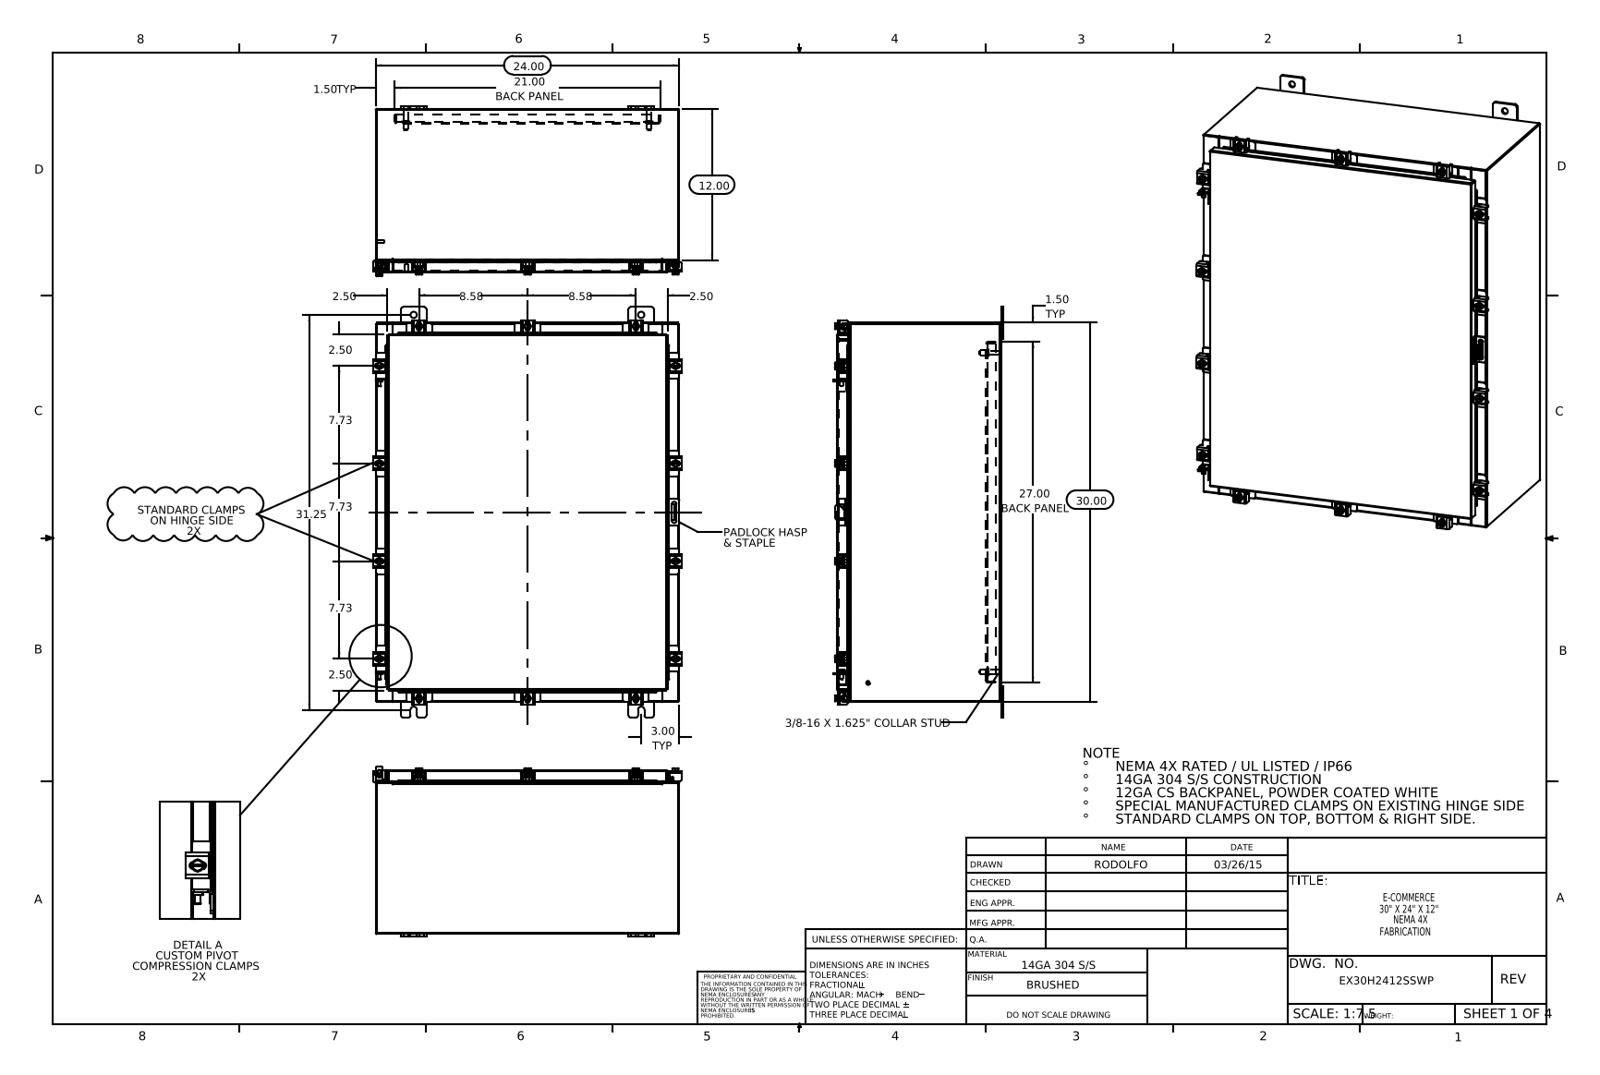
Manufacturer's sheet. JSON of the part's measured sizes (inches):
{"part_name": "Quarter-20 CD Stud; EX30H2412SSWP Cover; Clamp Top_RTP31; EX30H2412SSWP (+8 more)", "step_written_by": "SolidWorks 2014 (CONFIG_CONTROL_DESIGN)", "units": "inches", "bodies": {"solids": 91, "faces": 2272, "planar": 1211, "cylindrical": 885, "other": 176}, "overall_size": [32.5, 24.421, 13.453], "volume_in3": 296.7, "surface_area_in2": 7434, "round_holes": [[0.213, 14], [0.26, 14], [0.5, 8], [0.125, 1], [0.25, 1]], "round_bosses_or_shafts": [[0.5, 14], [0.25, 14], [0.399, 12], [0.625, 4], [0.375, 4], [0.33, 4], [0.315, 2], [0.236, 2]], "partial_cylinders_radius": [[0.06, 62], [0.141, 28], [0.013, 26], [0.12, 26], [0.19, 24], [0.088, 22], [0.09, 20], [0.05, 19]], "face_to_face_distances": [0.075, 12.9, 23.925, 12.975, 12.826, 0.104, 1, 29.925, 1.075, 11.826], "hole_center_spacings": [2.347, 4.44, 20.544, 23.451, 24.31, 26.507, 27.37, 32.286]}
